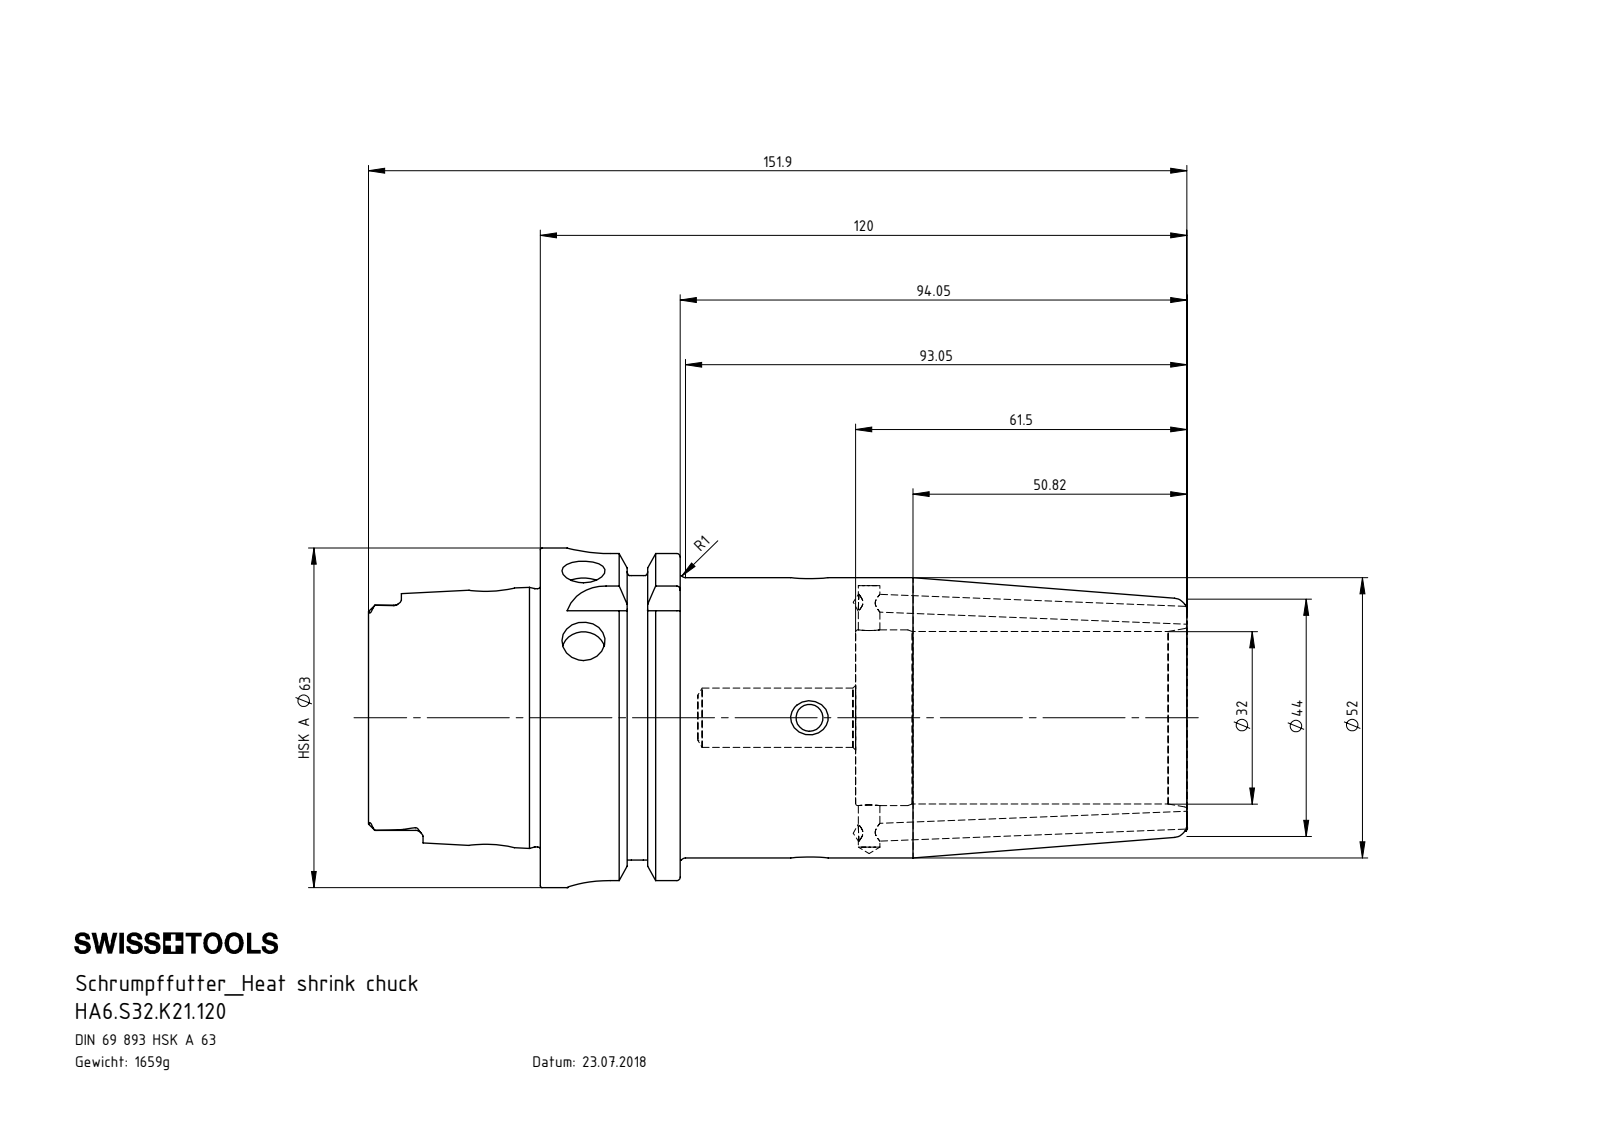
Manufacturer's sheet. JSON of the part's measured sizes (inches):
{"part_name": "HA6-S32.K21.120; ERU-CJ3.001.008; ERU-AN5.K01.020_A; HA6-S32.K21.120_C_Fertigbearbeitung", "step_written_by": "SolidWorks 2012 (CONFIG_CONTROL_DESIGN)", "units": "inches", "bodies": {"solids": 4, "faces": 296, "planar": 102, "cylindrical": 83, "other": 111}, "overall_size": [5.984, 2.48, 2.48], "volume_in3": 12.89, "surface_area_in2": 73.43, "round_holes": [[0.13, 2], [0.197, 2], [0.315, 2], [0.157, 1], [0.236, 1], [0.295, 1], [0.331, 1], [0.394, 1], [0.433, 1], [0.669, 1], [0.748, 1], [1.26, 1]], "round_bosses_or_shafts": [[0.157, 2], [2.48, 1], [2.163, 1], [2.047, 1], [1.887, 1], [0.472, 1]], "partial_cylinders_radius": [[0.055, 6], [0.113, 4], [0.315, 4]], "face_to_face_distances": [2.303, 1.281, 0.63, 1.022, 0.392, 1.911, 1.256, 1.648, 2.278, 3.559], "hole_center_spacings": [0.435, 1.691, 2.321, 2.756]}
